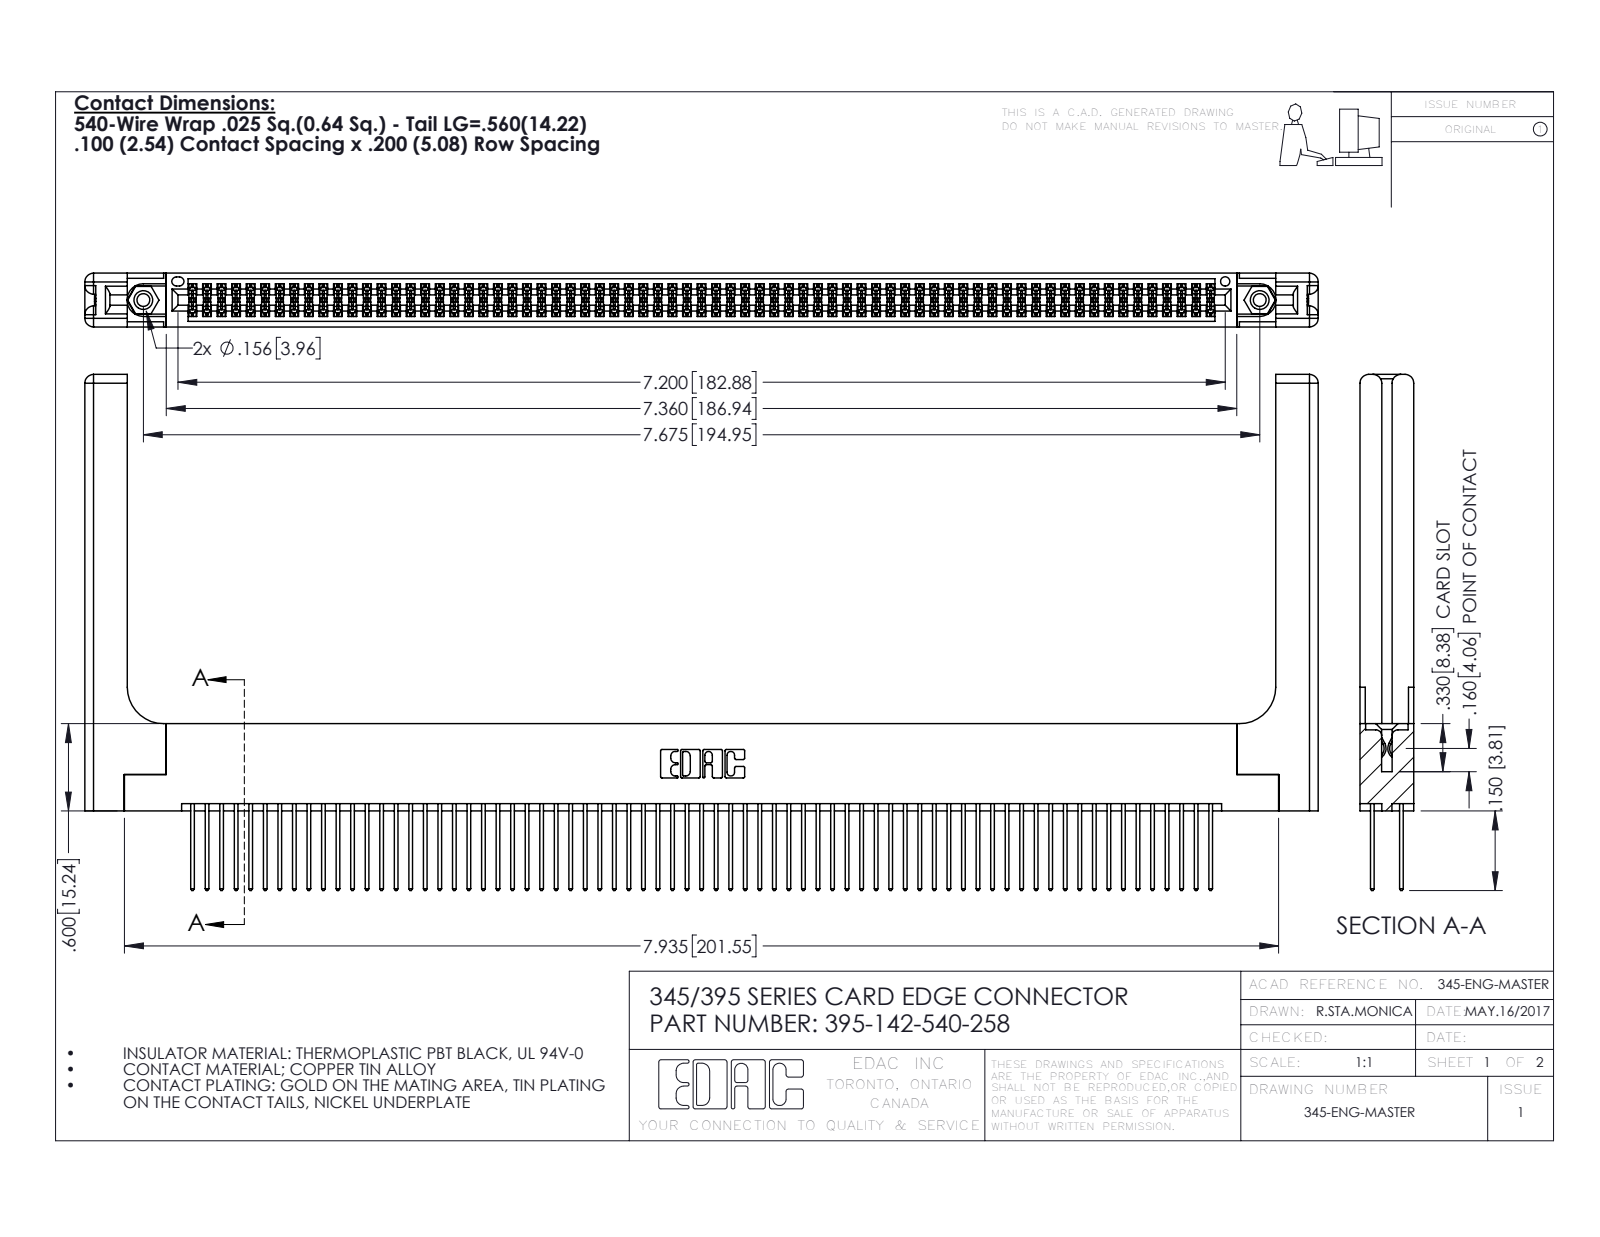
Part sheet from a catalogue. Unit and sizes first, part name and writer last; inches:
Units: inches
Overall size (bounding box): 8.479 × 3.547 × 0.37
Round holes (diameter × count): ⌀0.089 ×2, ⌀0.125 ×2, ⌀0.156 ×2, ⌀0.064 ×1
Round bosses / shafts (diameter × count): ⌀0.155 ×2
Partial cylindrical surfaces — rounded edges, fillets, slot ends (radius × count): R0.006 ×213, R0.01 ×142, R0.01 ×22, R0.06 ×16, R0.007 ×6, R0.031 ×6, R0.026 ×3, R0.014 ×2
Main face-to-face distances: 0.072, 0.298, 0.2, 0.37, 0.098, 0.272, 0.025, 0.225, 0.175, 0.148
Hole centre spacings: 0.27, 7.439, 7.675
Volume: 1.843 in³ · Surface area: 62.37 in²
Bodies: 147 solids, 7482 faces (4914 planar, 2508 cylindrical, 60 other)
Part name (STEP PRODUCT): 345-292-001_345-293-140; 345-220-058_345-220-058; 395-142-540-258; 345-250-001_345-250-001-102 (+1 more)
STEP written by: SolidWorks 2016 (CONFIG_CONTROL_DESIGN)
